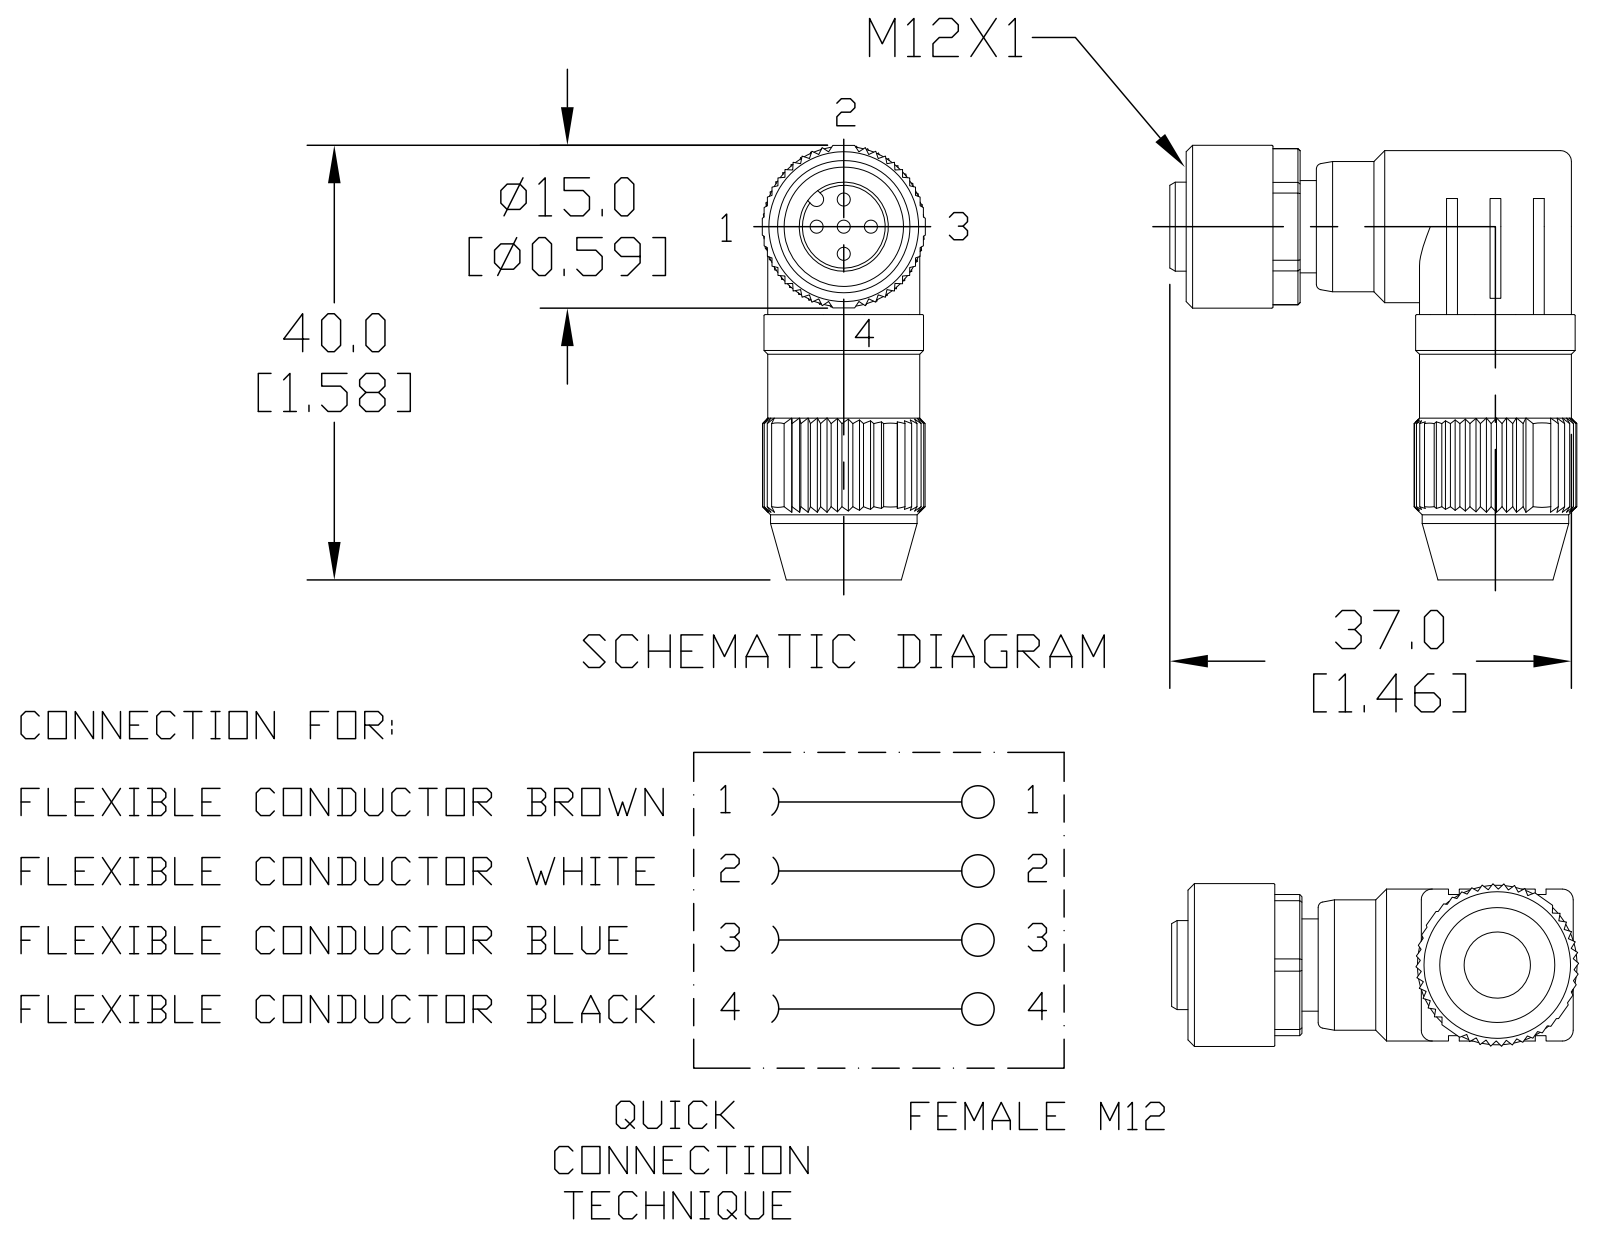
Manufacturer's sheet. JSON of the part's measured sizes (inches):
{"part_name": "7000-12681-0000000", "step_written_by": "SolidWorks 2015 (AUTOMOTIVE_DESIGN)", "units": "inches", "bodies": {"solids": 1, "faces": 356, "planar": 224, "cylindrical": 76, "other": 56}, "overall_size": [1.575, 1.457, 0.591], "volume_in3": 0.565, "surface_area_in2": 7.395, "round_holes": [[0.039, 5], [0.27, 1], [0.394, 1]], "round_bosses_or_shafts": [[0.591, 2], [0.545, 1], [0.541, 1], [0.525, 1], [0.508, 1], [0.359, 1], [0.32, 1]], "partial_cylinders_radius": [[0.02, 4], [0.021, 1]], "face_to_face_distances": [0.387, 0.97, 0.367, 0.517, 0.591, 0.398, 0.94, 0.03, 0.394, 0.397], "hole_center_spacings": [0.098, 0.139, 0.197]}
